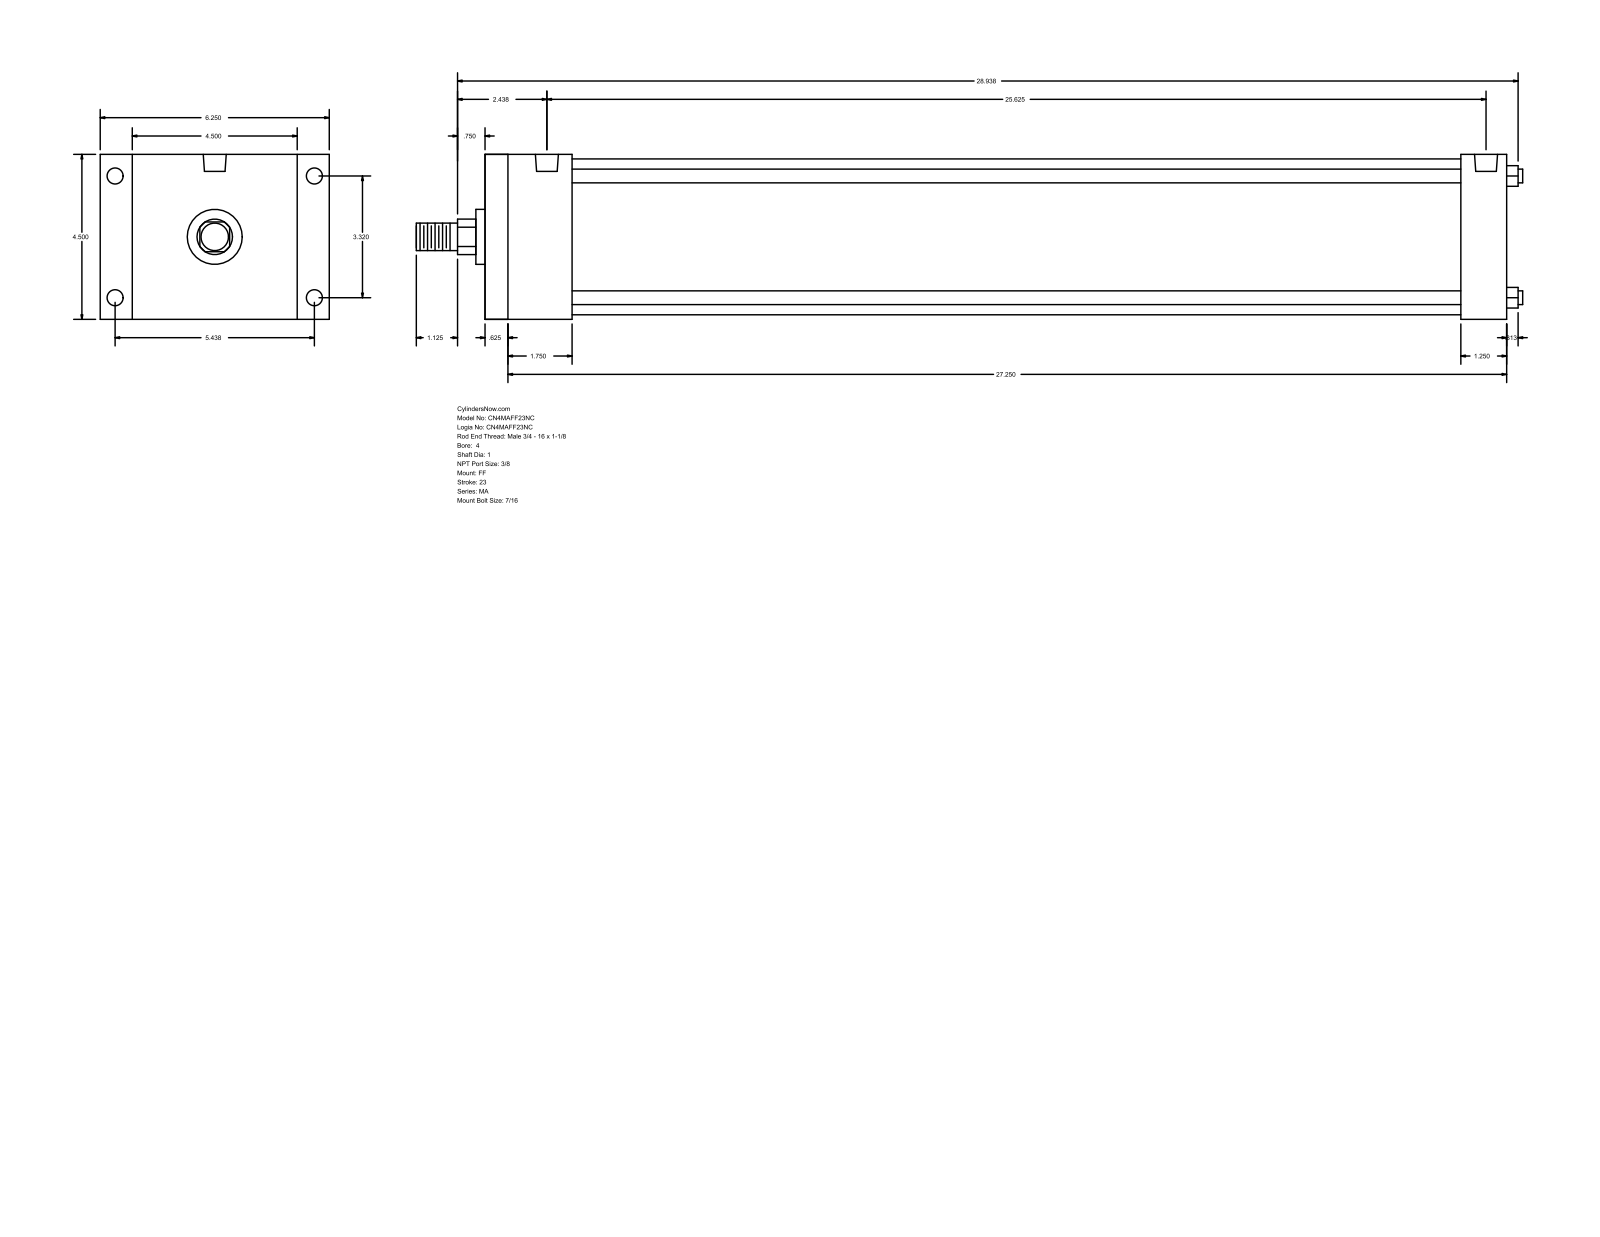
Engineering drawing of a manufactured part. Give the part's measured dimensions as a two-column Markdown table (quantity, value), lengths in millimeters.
| quantity | value |
| --- | --- |
| part name | MA_FF__0400_1 |
| STEP written by | GSSL Pune (CONFIG_CONTROL_DESIGN) |
| units | millimeters |
| bodies | 0 solids, 92 faces (64 planar, 28 cylindrical, 0 other) |
| overall size | 766.76 × 158.75 × 114.3 |
| round holes (diameter × count) | 11.11 × 8, 15.93 × 2 |
| round bosses / shafts (diameter × count) | 9.53 × 4, 107.95 × 1, 38.1 × 1, 25.4 × 1, 19.05 × 1 |
| partial cylindrical surfaces (radius × count) | 12.29 × 1 |
| main face-to-face distances | 114.3, 708.03, 15.87, 692.16, 22.23, 136.53, 676.28, 660.41, 31.75, 60.33 |
| hole center spacings | 84.32, 138.12, 161.82, 641.35, 4.76, 4.77, 646.11, 646.12 |
